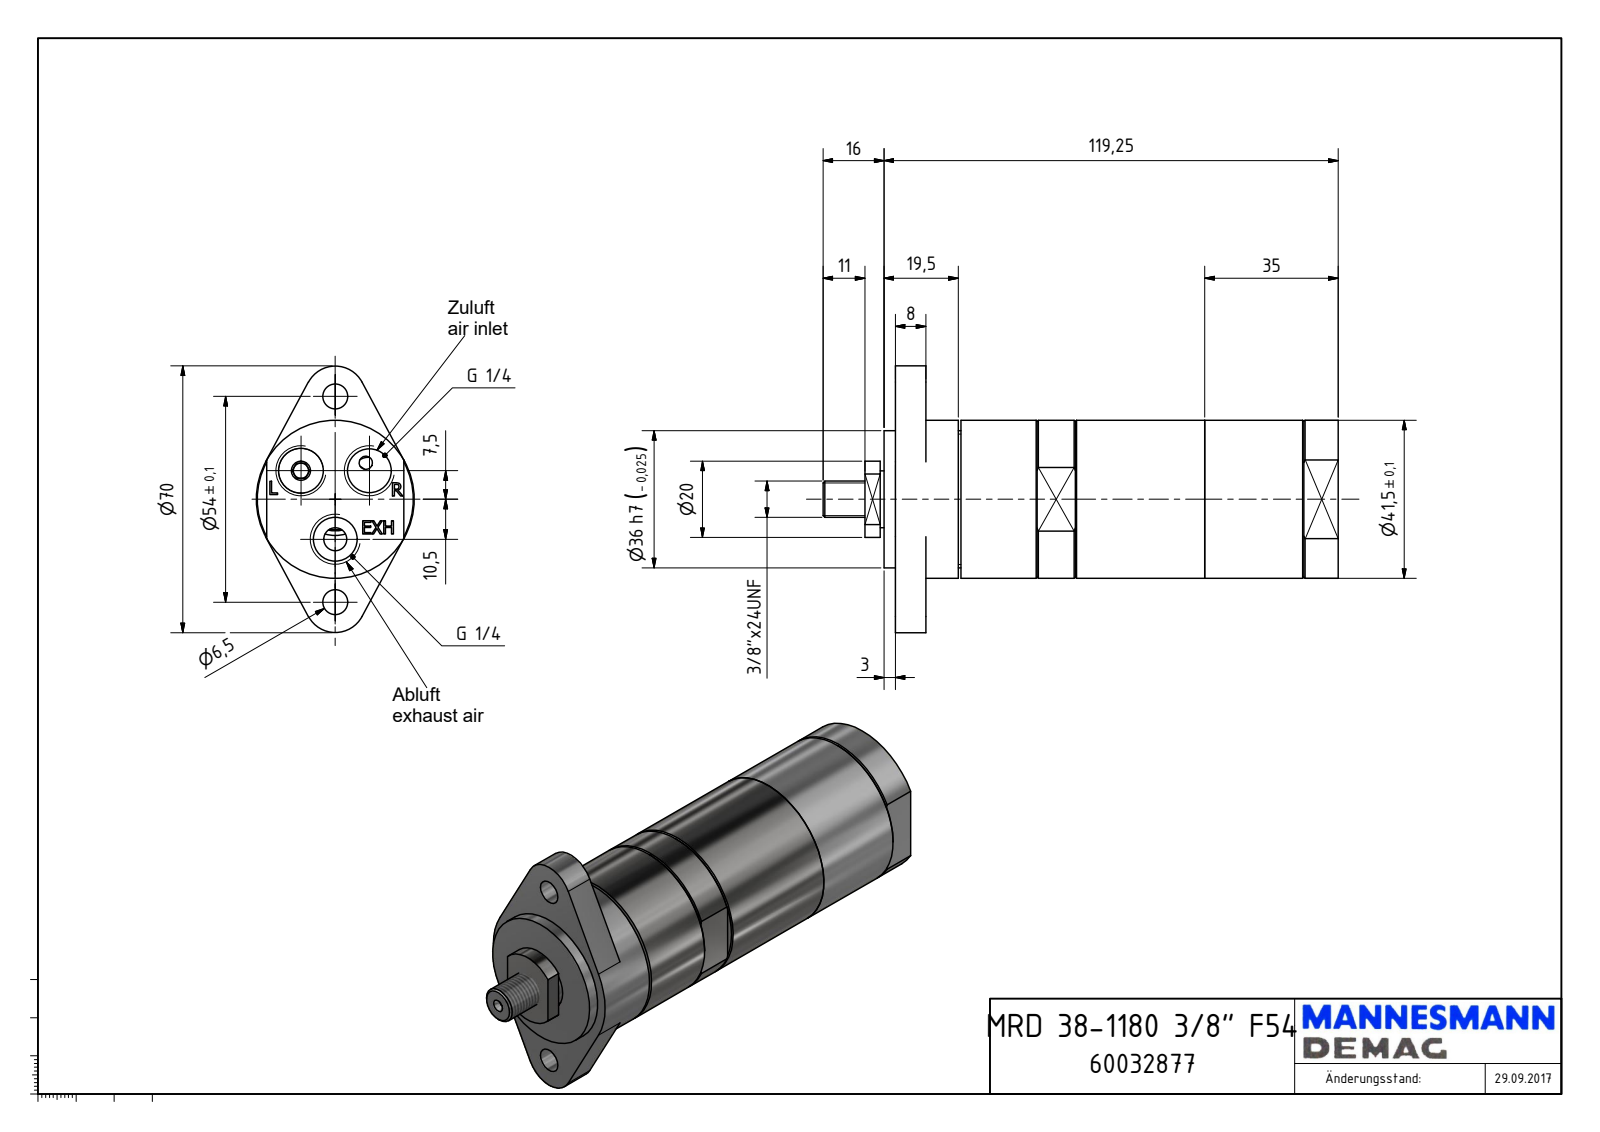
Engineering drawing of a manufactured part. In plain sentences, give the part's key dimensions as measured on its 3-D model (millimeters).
The part is named "MRD 38-1180 3-8 F54_60032877". Its 3-D file was written by "Autodesk Inventor 2018 (AUTOMOTIVE_DESIGN)". It is 1 solid with 152 faces: 103 planar, 24 cylindrical and 25 other. Overall it measures 135.25 by 70 by 41.5 millimeters. Its volume is 162 642 cubic millimeters and its surface area 22 564 square millimeters. Round holes: 3 of diameter 11.45, 2 of diameter 6.5, 1 of diameter 1.6, 1 of diameter 4, 1 of diameter 16. Round bosses or shafts: 1 of diameter 41.5, 1 of diameter 36, 1 of diameter 14.95, 1 of diameter 9.53. Partial cylindrical surfaces (rounded edges, fillets, slot ends): 2 of radius 8, 1 of radius 10. The main face-to-face distances are 116.25, 3, 119.25, 8, 11, 108.25, 1, 41.48, 16.5, 19.5. The hole center spacings are 11.72, 20.12, 21.48, 27, 35.65, 10.5, 16.5, 18.
